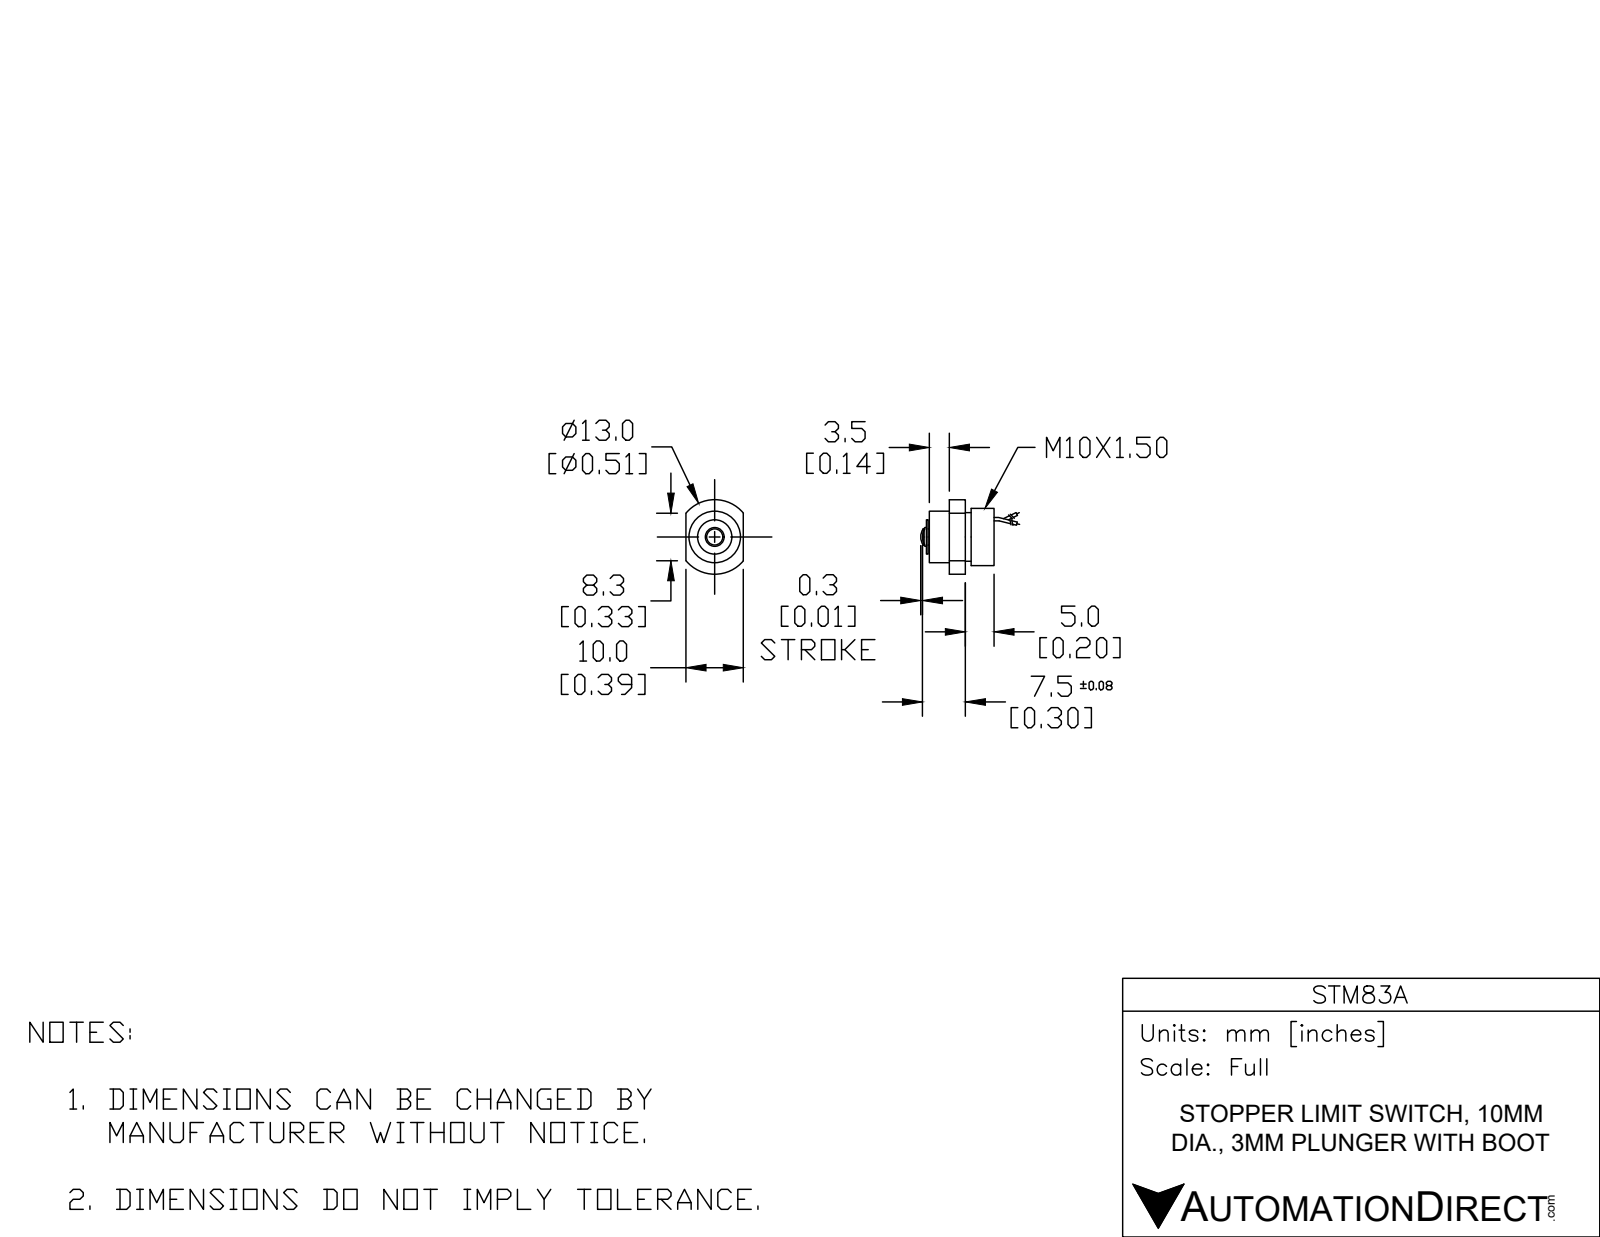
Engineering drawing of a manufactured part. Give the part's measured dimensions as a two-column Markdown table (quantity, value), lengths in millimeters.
| quantity | value |
| --- | --- |
| part name | STM83A |
| STEP written by | SolidWorks 2016 (CONFIG_CONTROL_DESIGN) |
| units | millimeters |
| bodies | 1 solid, 42 faces (13 planar, 22 cylindrical, 7 other) |
| overall size | 22.8 × 13 × 10 |
| volume | 883 mm³ |
| surface area | 769 mm² |
| round bosses / shafts (diameter × count) | 0.6 × 2, 10 × 1, 9 × 1, 8.34 × 1, 6 × 1, 2.8 × 1 |
| partial cylindrical surfaces (radius × count) | 6.5 × 1 |
| main face-to-face distances | 7.8, 5, 6.3, 11.3, 3.5, 2.8, 4, 10, 3.7, 6.5 |
